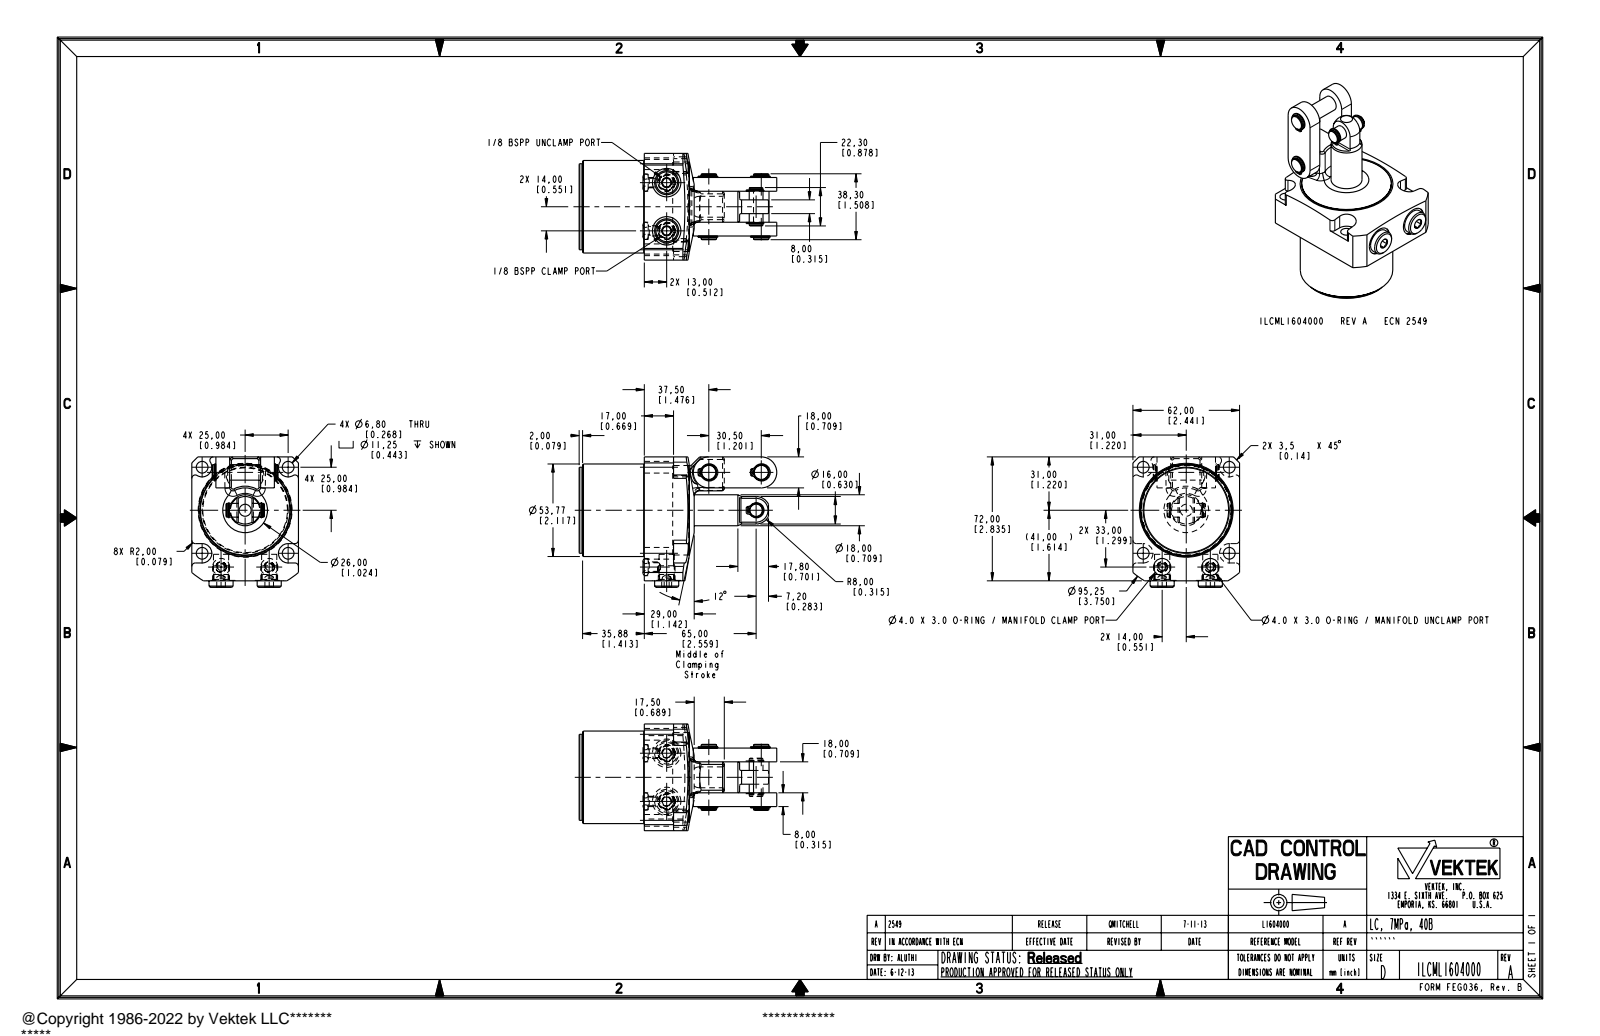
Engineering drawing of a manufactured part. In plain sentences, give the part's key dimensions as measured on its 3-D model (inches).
The part is named "ILCML1604000_BODY; ILCML1604000_LUG; ILCML1604000_ASM". Its 3-D file was written by "PRO/ENGINEER BY PARAMETRIC TECHNOLOGY CORPORATION, 2007460 (AUTOMOTIVE_DESIGN_CC2)". It is 4 solids with 385 faces: 139 planar, 173 cylindrical and 73 other. Overall it measures 4.523 by 2.985 by 2.441 inches. Its volume is 13.72 cubic inches and its surface area 66.01 square inches. Round holes: 6 of diameter 0.041, 4 of diameter 0.197, 4 of diameter 0.268, 2 of diameter 0.348, 2 of diameter 0.394, 2 of diameter 0.65, 1 of diameter 2.047. Round bosses or shafts: 2 of diameter 0.551, 2 of diameter 0.393, 2 of diameter 0.383, 2 of diameter 0.354, 2 of diameter 0.33, 2 of diameter 0.325, 2 of diameter 0.236, 1 of diameter 2.117. Partial cylindrical surfaces (rounded edges, fillets, slot ends): 10 of radius 0.079, 6 of radius 0.041, 4 of radius 0.069, 4 of radius 0.221, 2 of radius 0.031, 2 of radius 0.091, 2 of radius 0.354, 1 of radius 0.172. The main face-to-face distances are 2.141, 1.491, 0.65, 0.551, 2.441, 1.89, 0.315, 0.866, 1.575, 1.024. The hole center spacings are 1.392, 1.969, 0.092, 0.535, 0.872, 1.102, 1.201, 1.204.
